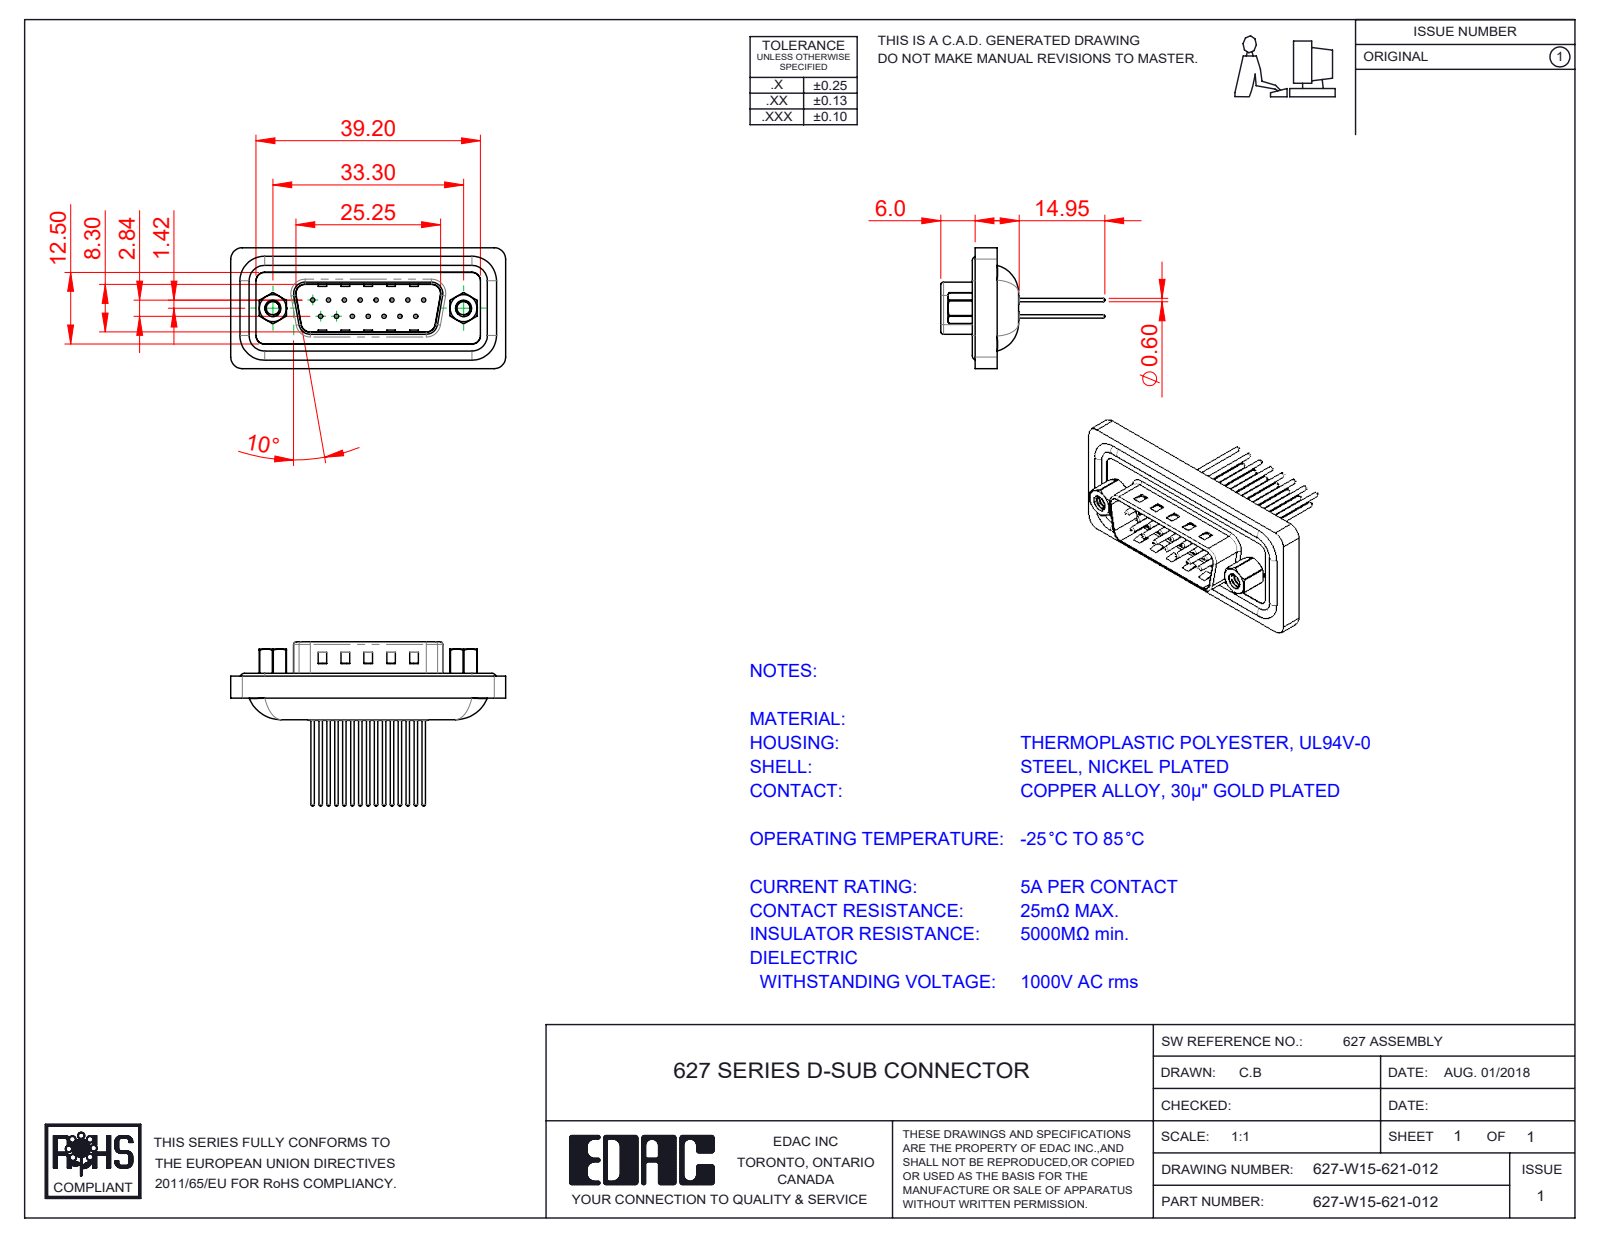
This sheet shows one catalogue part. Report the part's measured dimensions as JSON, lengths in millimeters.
{"part_name": "627W Contact Row 2_21; 627W 4-40 Threaded Rivet; 627W Housing_15 Contacts; 627W Waterproof Housing_15 Contacts (+4 more)", "step_written_by": "SolidWorks 2020 (CONFIG_CONTROL_DESIGN)", "units": "millimeters", "bodies": {"solids": 23, "faces": 1069, "planar": 278, "cylindrical": 456, "other": 335}, "overall_size": [48, 28.65, 21.1], "volume_mm3": 5804, "surface_area_mm2": 8601, "round_holes": [[0.75, 15], [1.5, 15], [1.6, 15], [2, 15], [2.26, 2], [2.29, 2], [4, 2], [4.8, 2], [5, 2]], "round_bosses_or_shafts": [[0.6, 15], [1.5, 7], [1.6, 4], [4.9, 2], [2.79, 2]], "partial_cylinders_radius": [[2, 16], [1.5, 14], [0.5, 8], [2.7, 6], [0.9, 4], [1.6, 4], [4.3, 4], [0.4, 2]], "face_to_face_distances": [0.75, 0.4, 1.1, 2.75, 3.75, 0.5, 1.85, 4.6, 1.6, 1], "hole_center_spacings": [3.16, 2.77, 5.54, 8.31, 5.03, 5.04, 7.48, 7.49]}
